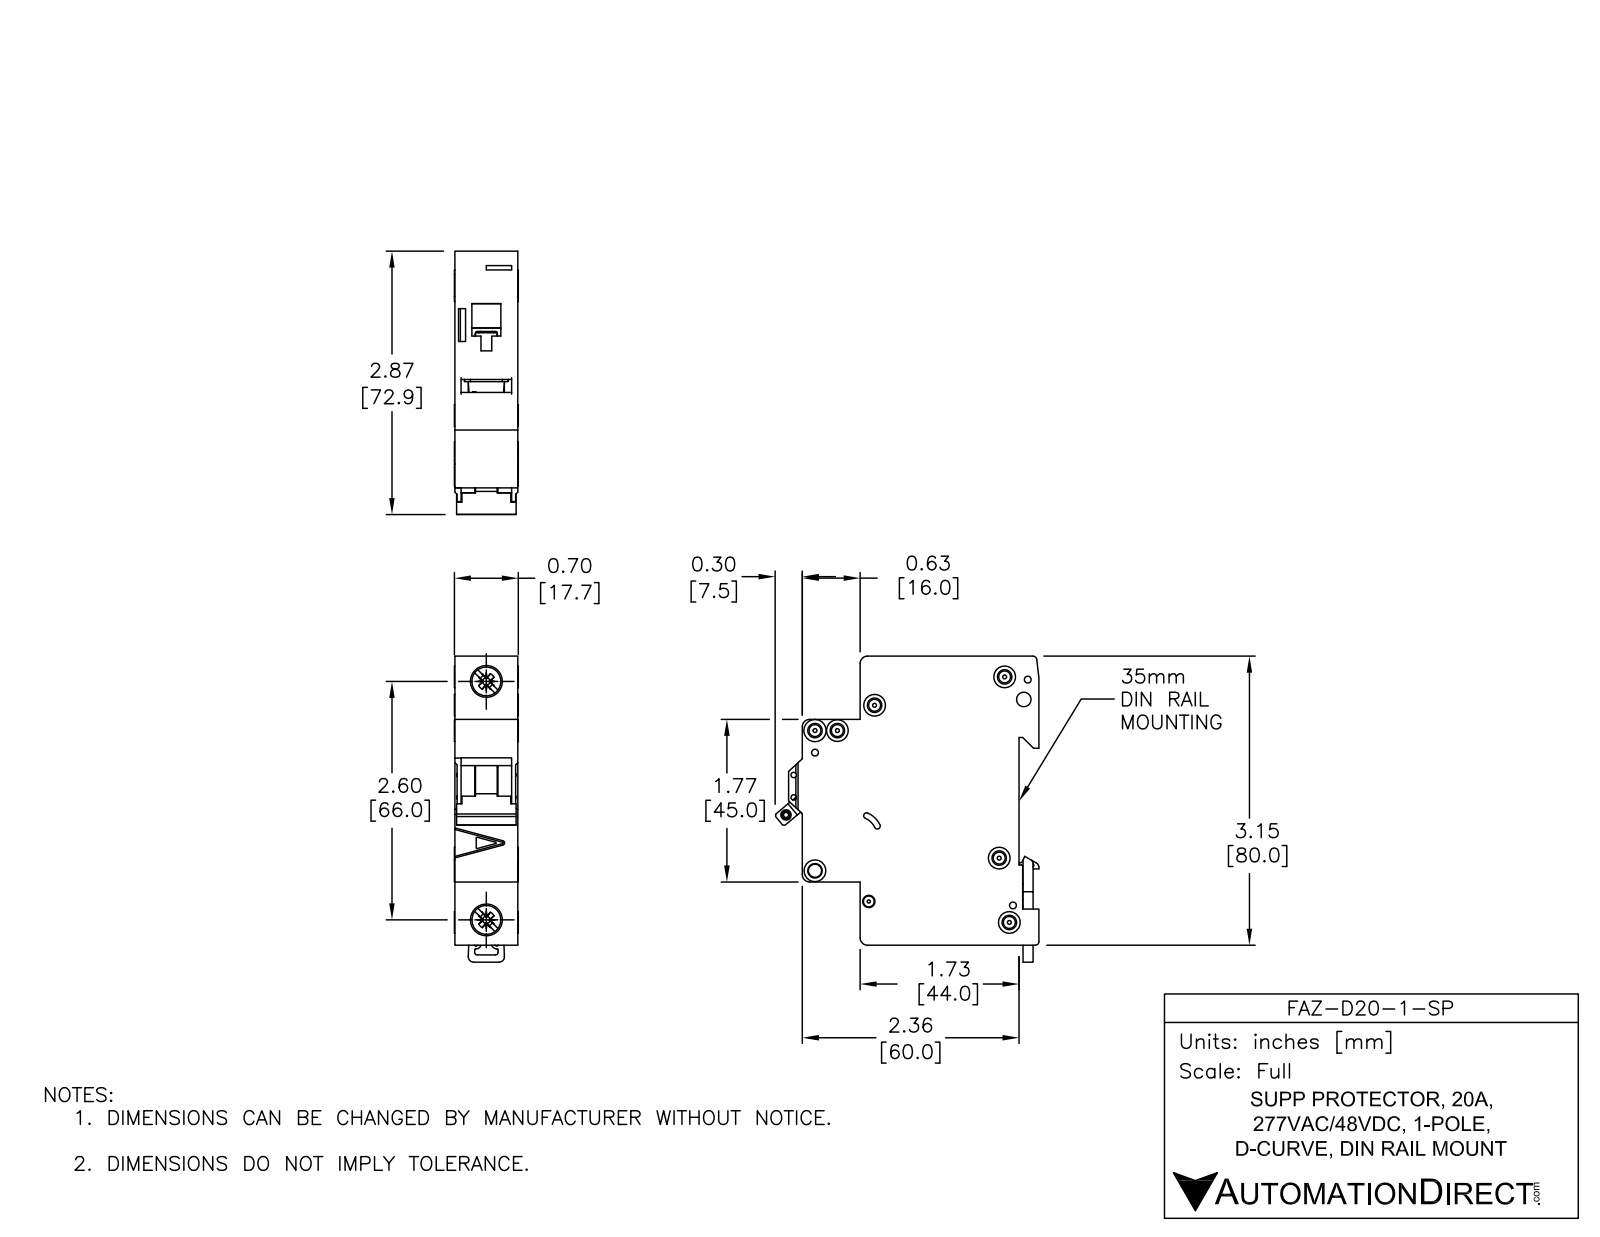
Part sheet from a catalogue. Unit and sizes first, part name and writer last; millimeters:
Units: millimetres
Overall size (bounding box): 84.78 × 73.04 × 17.7
Round holes (diameter × count): ⌀3.6 ×6, ⌀1.9 ×3, ⌀1.09 ×2, ⌀1.5 ×2, ⌀4 ×2, ⌀7.15 ×2, ⌀2.15 ×1, ⌀2.2 ×1, ⌀2.55 ×1, ⌀3.3 ×1, ⌀3.4 ×1
Round bosses / shafts (diameter × count): ⌀6 ×4, ⌀8.2 ×2, ⌀2.5 ×1
Partial cylindrical surfaces — rounded edges, fillets, slot ends (radius × count): R0.25 ×30, R0.5 ×13, R2 ×8, R0.2 ×5, R1 ×4, R0.8 ×2, R3 ×2, R1.5 ×1
Main face-to-face distances: 17.5, 79.48, 5.5, 49.5, 44, 65.5, 60, 16, 1.75, 15.75
Hole centre spacings: 6.2, 13.64, 4.81, 5.19, 5.61, 6.1, 6.44, 8.19
Volume: 74 935 mm³ · Surface area: 19 545 mm²
Bodies: 5 solids, 558 faces (235 planar, 202 cylindrical, 121 other)
Part name (STEP PRODUCT): FAZ-D20-1-SP
STEP written by: SolidWorks 2014 (AUTOMOTIVE_DESIGN)
